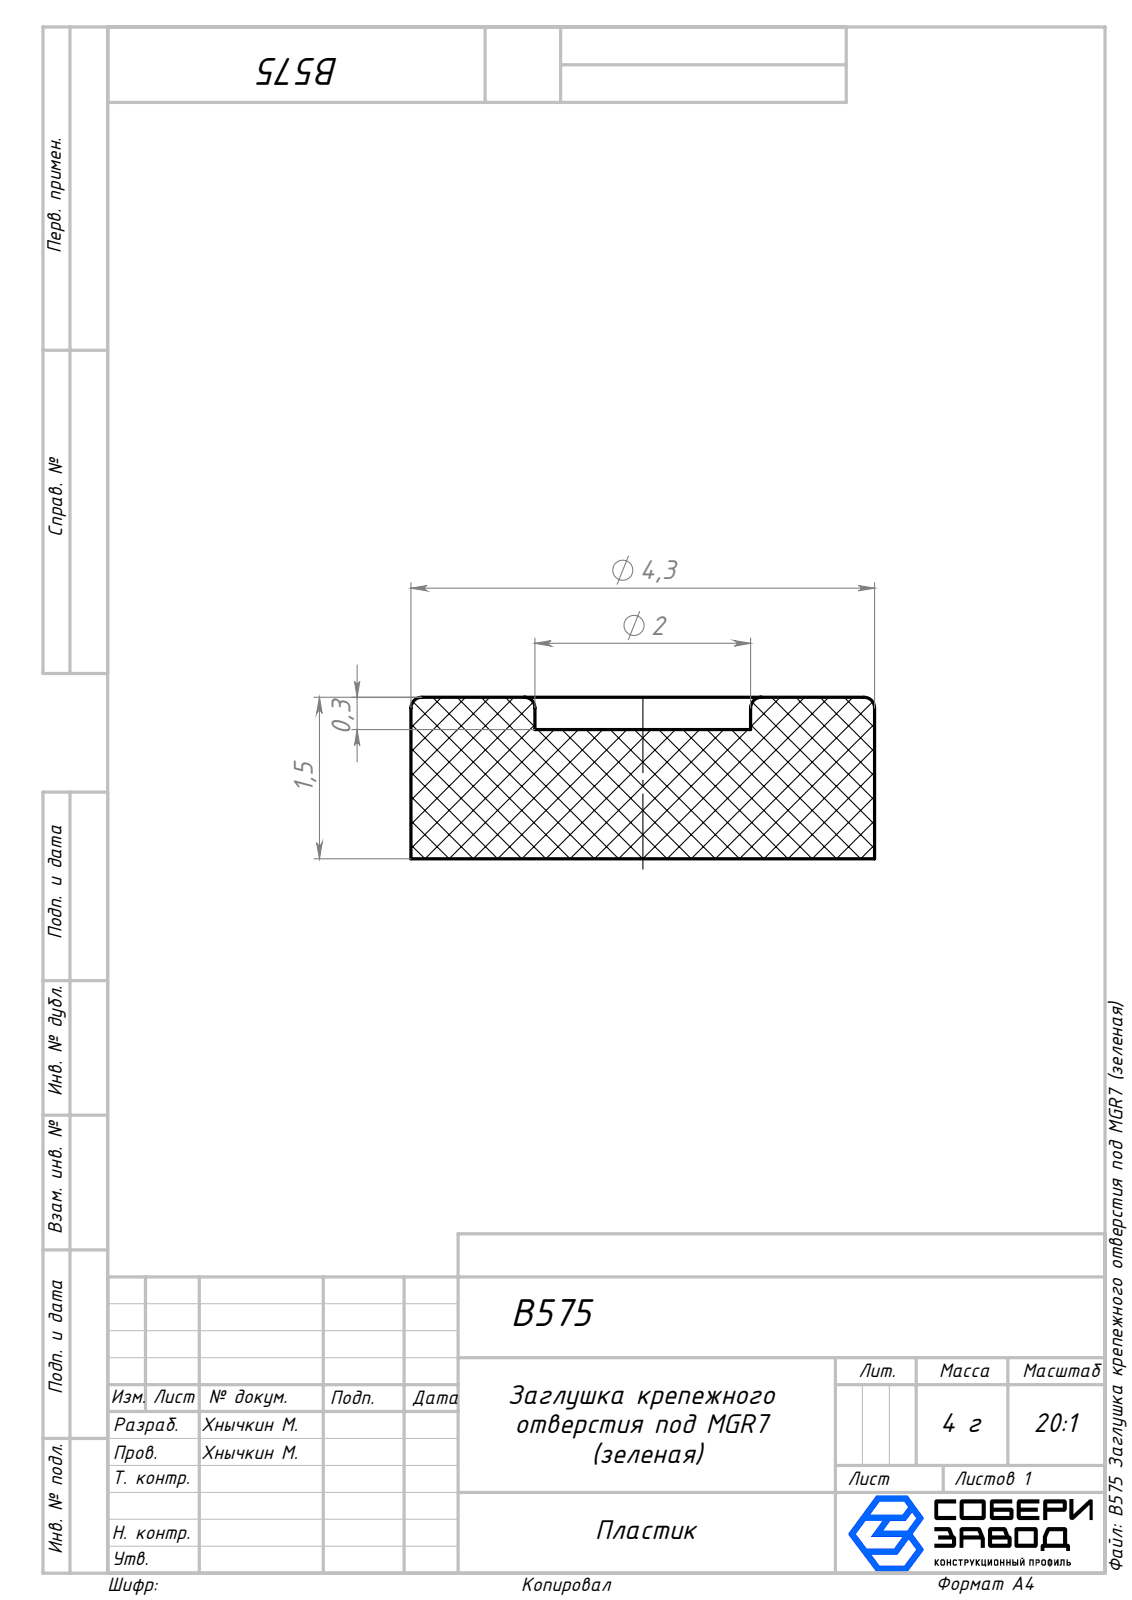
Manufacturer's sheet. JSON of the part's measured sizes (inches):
{"part_name": "B575 Заглушка крепежного отверстия под MGR7 (зеленая)", "step_written_by": "SolidWorks 2026 (AUTOMOTIVE_DESIGN)", "units": "inches", "bodies": {"solids": 1, "faces": 11, "planar": 3, "cylindrical": 4, "other": 4}, "overall_size": [0.169, 0.169, 0.059], "volume_in3": 0.001, "surface_area_in2": 0.078, "round_holes": [[0.079, 1]], "round_bosses_or_shafts": [[0.169, 1]], "face_to_face_distances": [0.059, 0.047]}
